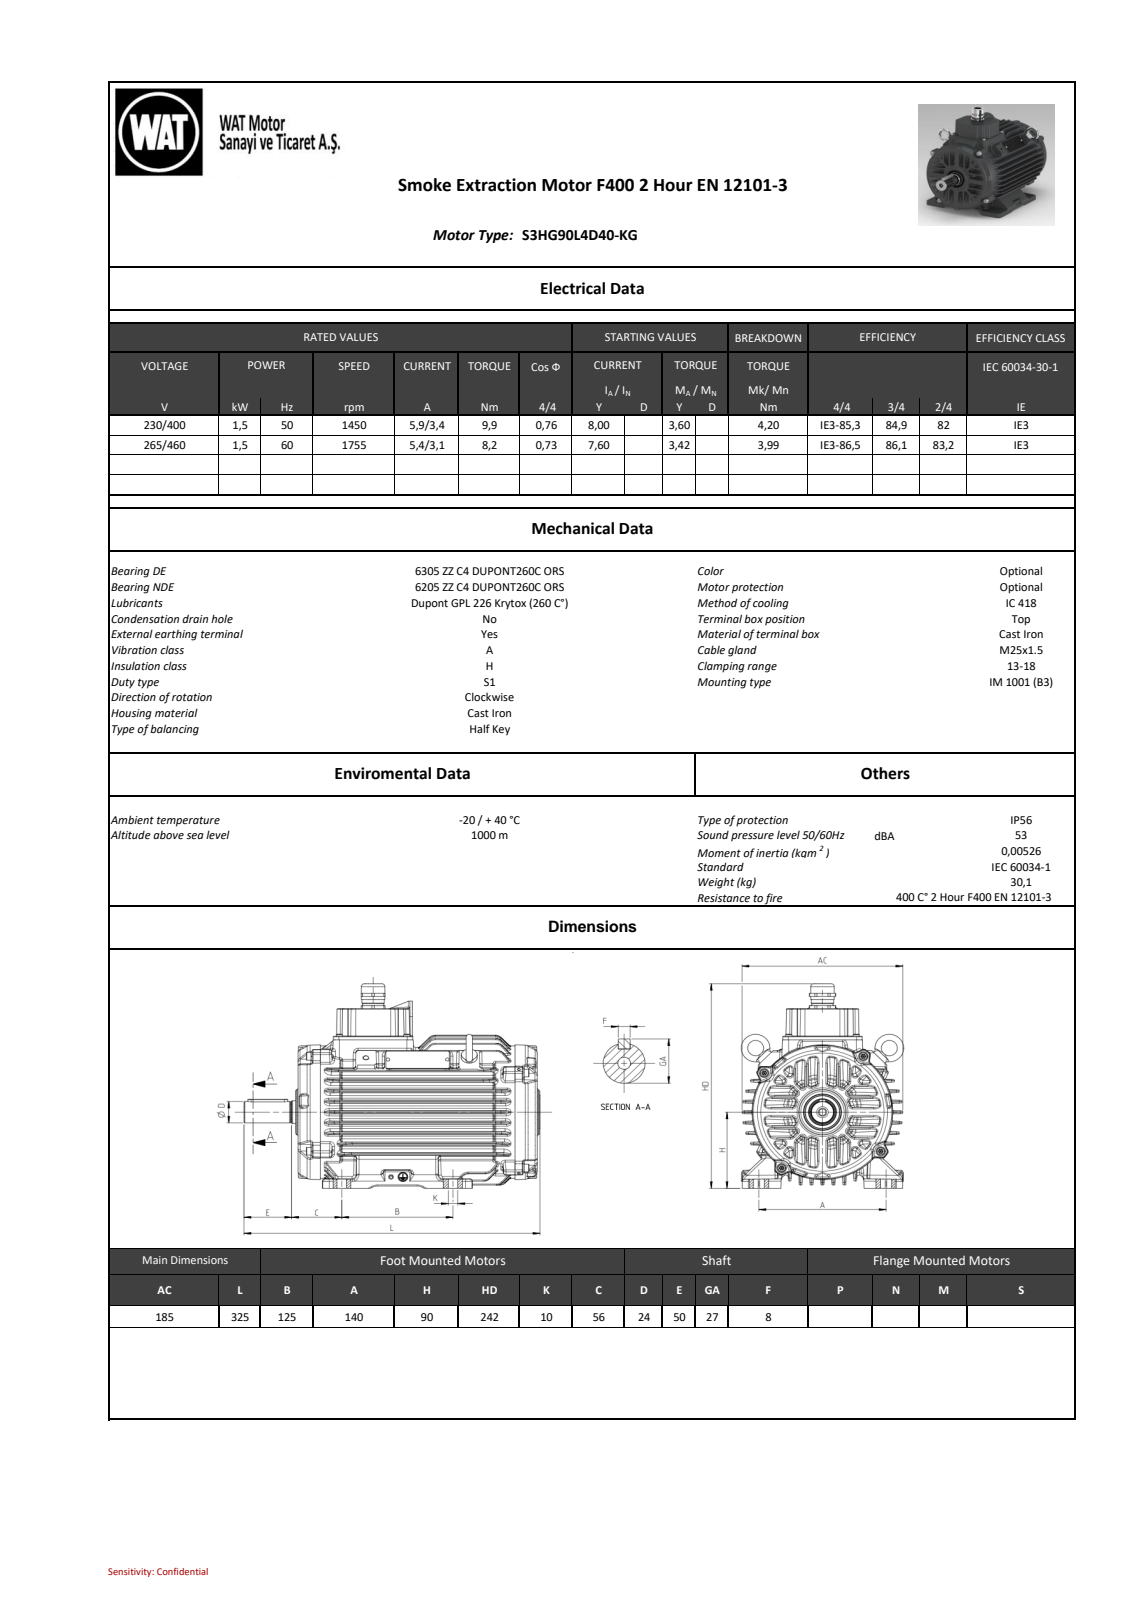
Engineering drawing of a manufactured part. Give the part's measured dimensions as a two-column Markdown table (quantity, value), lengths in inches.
| quantity | value |
| --- | --- |
| part name | 26032C0836B7xhhd |
| STEP written by | SIEMENS PLM Software NX 11.0 (AUTOMOTIVE_DESIGN) |
| units | inches |
| bodies | 0 solids, 4021 faces (751 planar, 976 cylindrical, 2294 other) |
| overall size | 12.807 × 9.519 × 8.896 |
| round holes (diameter × count) | 0.165 × 3, 0.098 × 2, 0.268 × 1, 0.331 × 1, 0.709 × 1, 1.26 × 1 |
| round bosses / shafts (diameter × count) | 0.315 × 4, 0.787 × 3, 0.362 × 3, 0.326 × 3, 0.197 × 3, 2.441 × 1, 1.165 × 1, 1.108 × 1 |
| partial cylindrical surfaces (radius × count) | 0.059 × 422, 0.039 × 31, 0.079 × 31, 0.157 × 22, 0.02 × 18, 0.197 × 14, 0.118 × 6, 0.394 × 6 |
| main face-to-face distances | 0.474, 10.296, 10.474, 0.177, 1.574, 8.682, 1.614, 1.791, 6.282, 7.856 |
| hole center spacings | 0.25, 2.953 |
